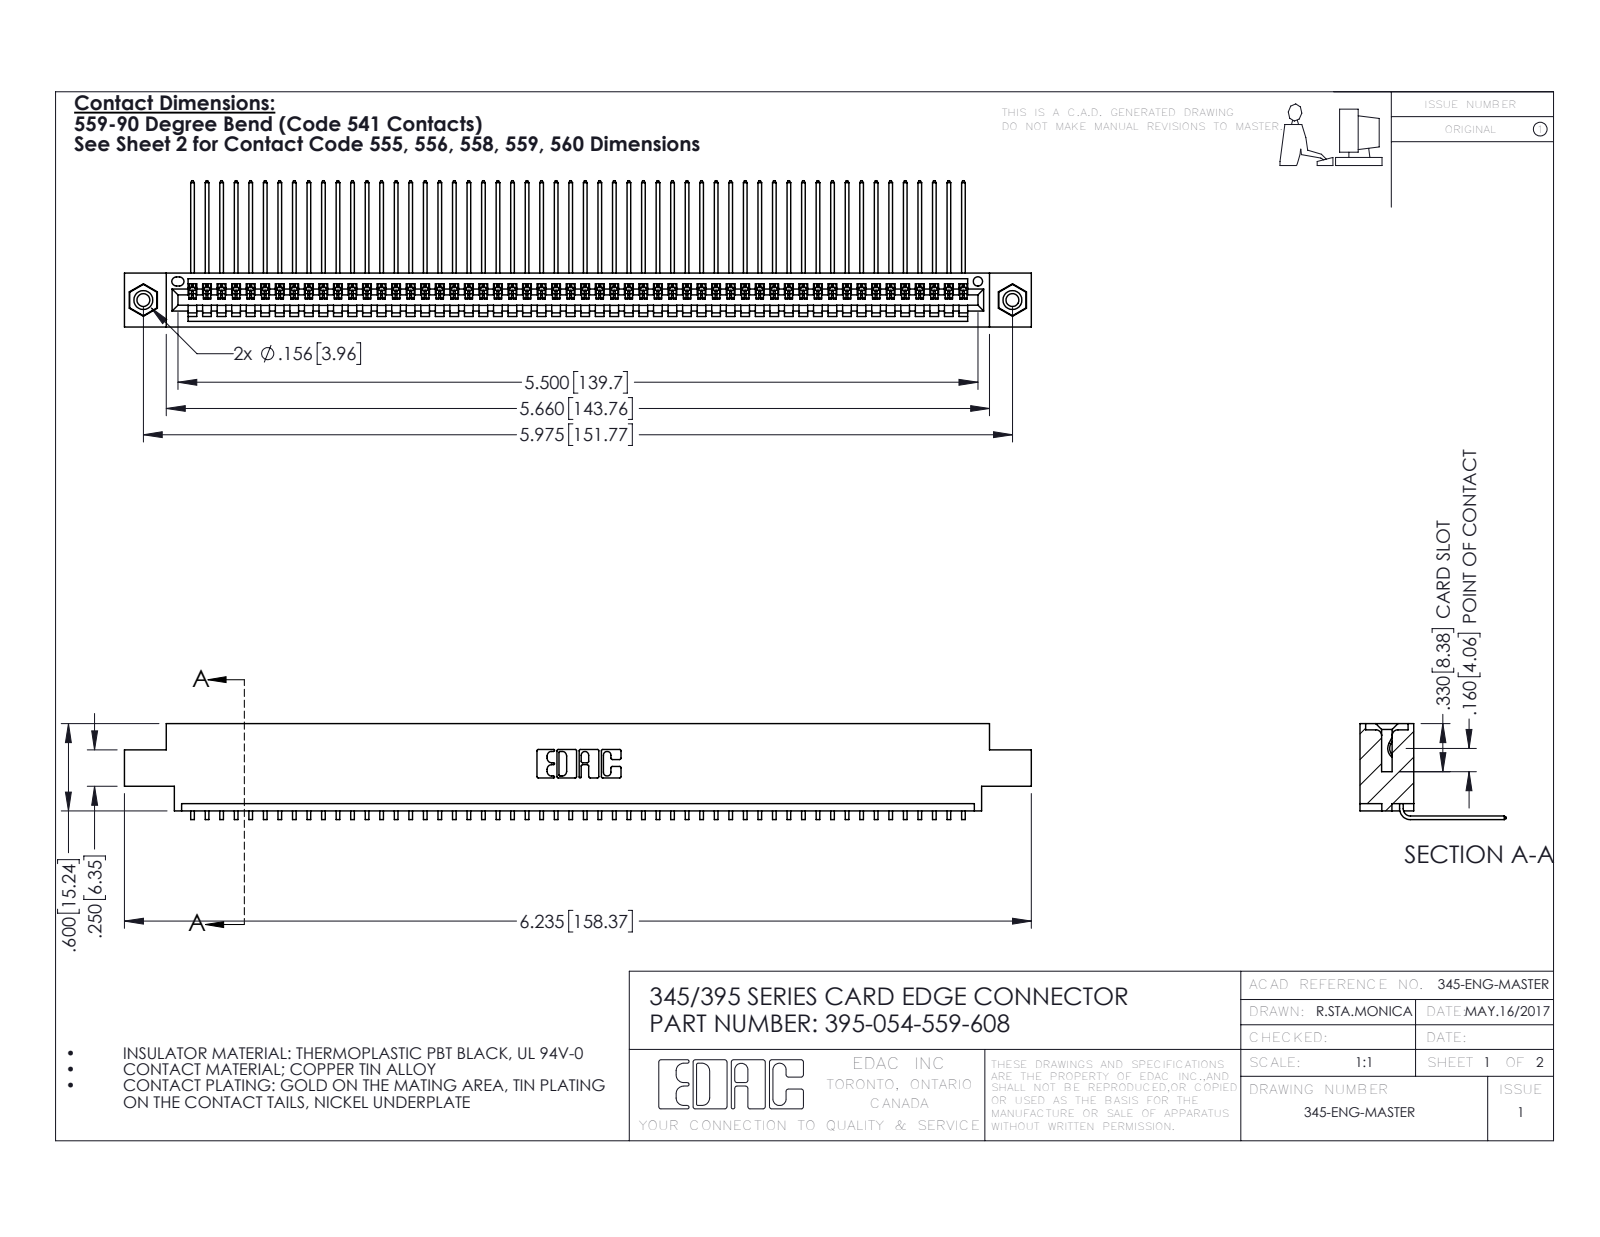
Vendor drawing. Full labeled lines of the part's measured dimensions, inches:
Part name (STEP PRODUCT): 345-250-001_345-250-003-102; 345 Part_0.170 Offset - 0.156 Dia-TI; 345-292-001_558 559 Tail - 1; 395-054-559-608
STEP written by: SolidWorks 2016 (CONFIG_CONTROL_DESIGN)
Units: inches
Bodies: 57 solids, 3430 faces (2384 planar, 1030 cylindrical, 16 other)
Overall size (bounding box): 6.235 × 1.005 × 0.659
Volume: 0.928 in³ · Surface area: 33.43 in²
Round holes (diameter × count): ⌀0.089 ×2, ⌀0.125 ×2, ⌀0.156 ×2, ⌀0.064 ×1
Round bosses / shafts (diameter × count): ⌀0.155 ×2
Partial cylindrical surfaces — rounded edges, fillets, slot ends (radius × count): R0.006 ×108, R0.01 ×22, R0.007 ×6, R0.031 ×6, R0.026 ×3, R0.031 ×2, R0.04 ×2, R0.014 ×1
Main face-to-face distances: 0.072, 0.298, 0.37, 0.2, 0.098, 0.272, 0.025, 0.225, 0.175, 0.149
Hole centre spacings: 0.27, 5.739, 5.975
